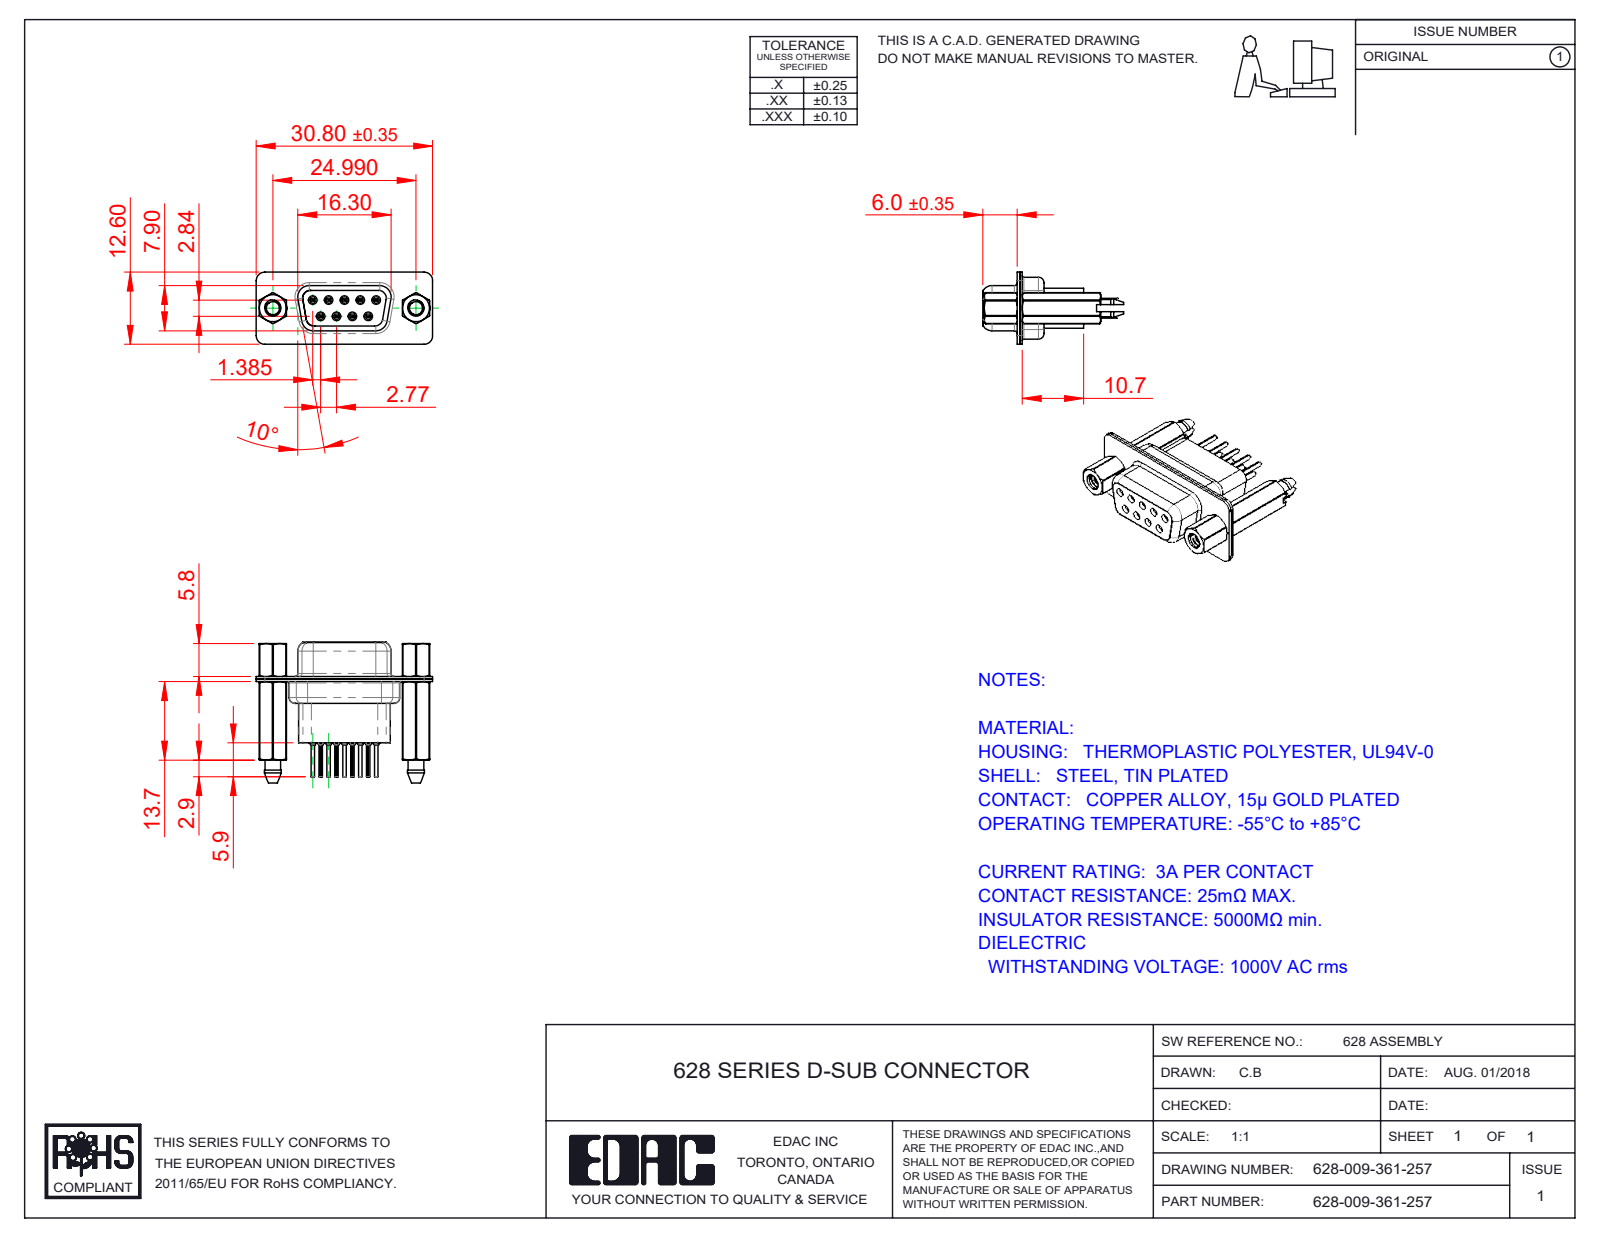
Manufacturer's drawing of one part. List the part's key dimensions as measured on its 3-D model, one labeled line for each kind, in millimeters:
Part name (STEP PRODUCT): 628 Contact Row 1_61; 628 Shell Rear_09 Contacts; 628-009-361-257; 628 Housing_09 HP (+4 more)
STEP written by: SolidWorks 2020 (CONFIG_CONTROL_DESIGN)
Units: millimetres
Bodies: 16 solids, 1586 faces (400 planar, 538 cylindrical, 648 other)
Overall size (bounding box): 30.8 × 24.6 × 12.6
Volume: 2 803 mm³ · Surface area: 6 511 mm²
Round holes (diameter × count): ⌀0.2 ×9, ⌀0.8 ×9, ⌀0.9 ×9, ⌀1.1 ×9, ⌀1.6 ×9, ⌀1.7 ×5, ⌀2.26 ×2, ⌀2.29 ×2, ⌀4 ×2, ⌀4.05 ×2, ⌀4.85 ×2
Round bosses / shafts (diameter × count): ⌀2 ×9, ⌀1.5 ×9, ⌀1.2 ×9, ⌀0.6 ×9, ⌀4.95 ×2, ⌀4.8 ×2, ⌀2.79 ×2
Partial cylindrical surfaces — rounded edges, fillets, slot ends (radius × count): R1.5 ×19, R0.1 ×18, R2 ×12, R0.28 ×9, R1.35 ×6, R1.6 ×6, R0.25 ×4, R0.5 ×4
Main face-to-face distances: 0.45, 0.4, 0.9, 4.76, 8.5, 6.6, 1.9, 1.4, 7, 0.5
Hole centre spacings: 3.16, 2.77, 5.54, 5.03, 5.04, 8.31, 7.48, 7.49
